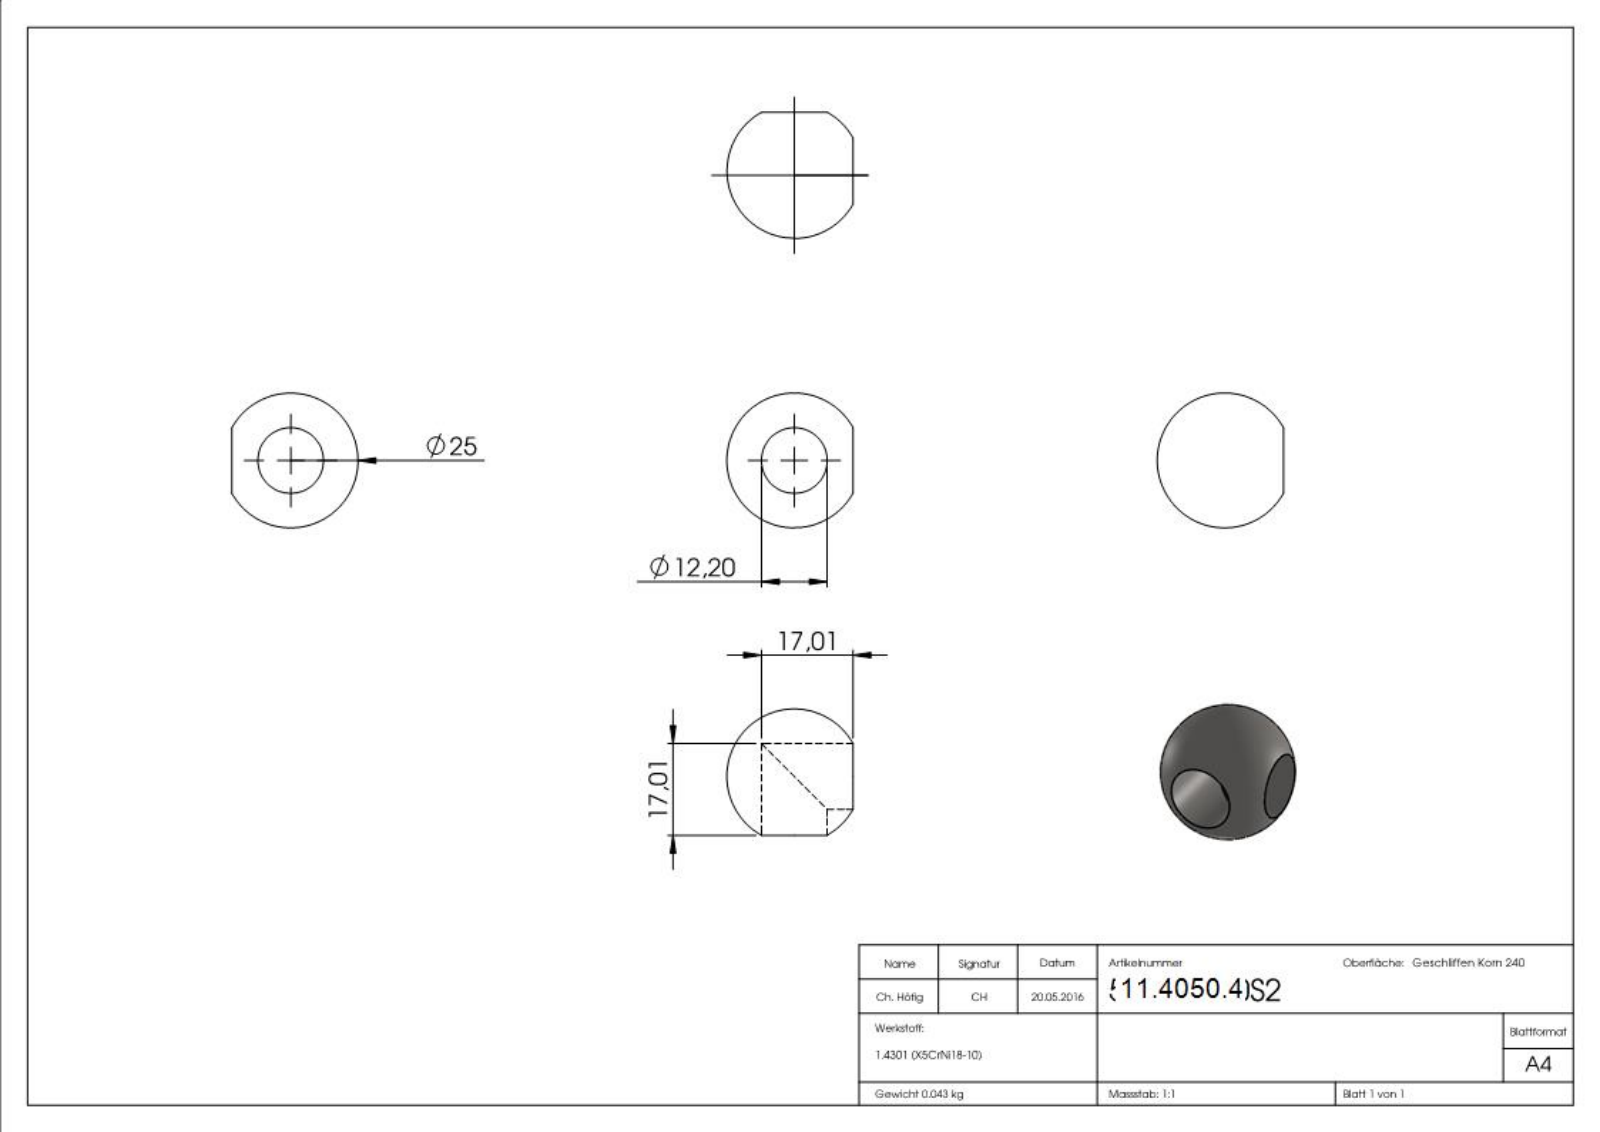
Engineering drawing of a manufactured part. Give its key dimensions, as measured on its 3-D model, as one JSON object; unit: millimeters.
{"part_name": "51025-240S2", "step_written_by": "SolidWorks 2015 (CONFIG_CONTROL_DESIGN)", "units": "millimeters", "bodies": {"solids": 1, "faces": 6, "planar": 0, "cylindrical": 4, "other": 2}, "overall_size": [25, 23.41, 23.41], "volume_mm3": 5440, "surface_area_mm2": 2550, "round_holes": [[12.2, 2]]}
